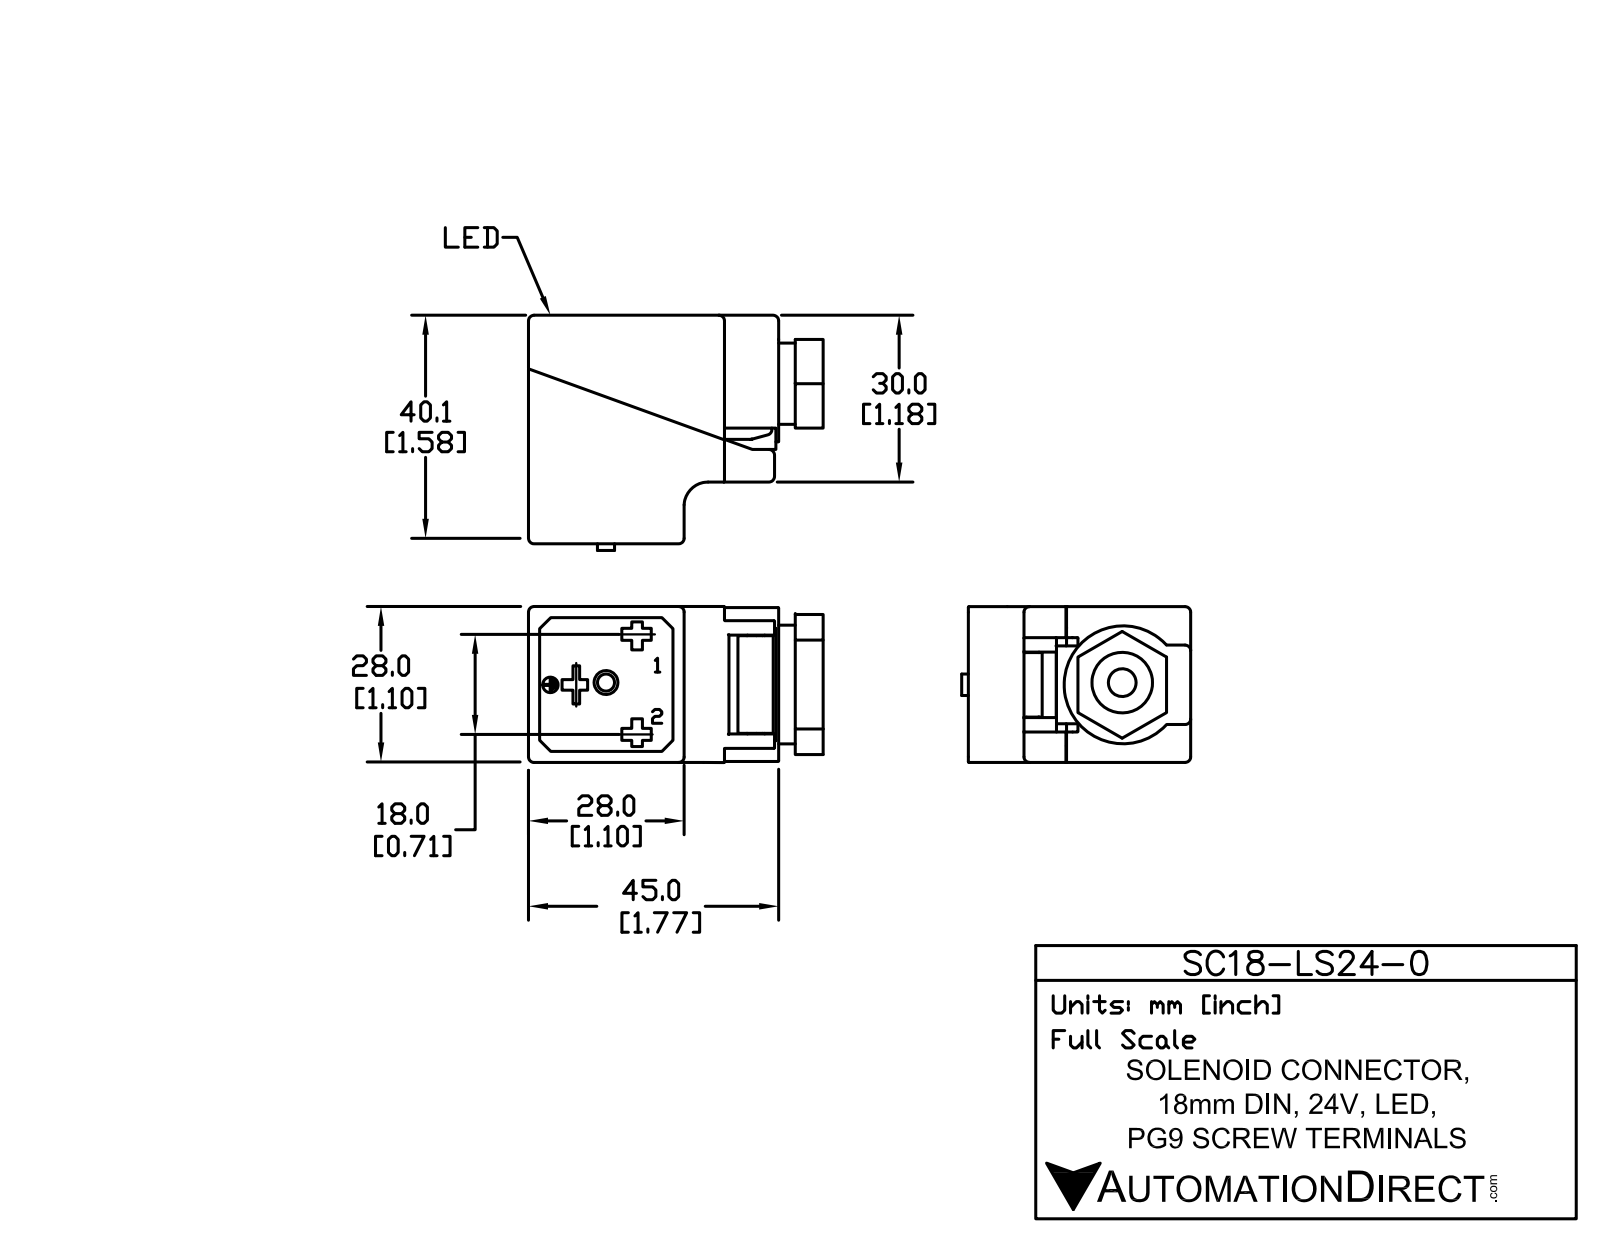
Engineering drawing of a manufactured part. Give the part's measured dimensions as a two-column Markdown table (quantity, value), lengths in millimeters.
| quantity | value |
| --- | --- |
| part name | SC18-LS24-0 |
| STEP written by | SolidWorks 2011 (AUTOMOTIVE_DESIGN) |
| units | millimeters |
| bodies | 7 solids, 501 faces (396 planar, 71 cylindrical, 34 other) |
| overall size | 53.55 × 46 × 28 |
| volume | 29 002 mm³ |
| surface area | 20 998 mm² |
| round holes (diameter × count) | 2.5 × 1, 3 × 1, 3.5 × 1, 3.75 × 1, 5.5 × 1, 5.75 × 1, 7 × 1, 9.4 × 1, 10 × 1, 10.1 × 1, 11 × 1, 14 × 1 |
| round bosses / shafts (diameter × count) | 1.5 × 2, 15 × 1, 13.5 × 1, 13.4 × 1, 11.7 × 1, 5.9 × 1, 3 × 1, 2.9 × 1 |
| partial cylindrical surfaces (radius × count) | 2 × 13, 1 × 12, 0.36 × 2, 1.5 × 2, 0.5 × 1, 1.36 × 1, 1.43 × 1, 1.5 × 1 |
| main face-to-face distances | 2.35, 23.3, 25.65, 2, 2.5, 2.3, 25.6, 2.15, 23.15, 27.95 |
| hole center spacings | 10.75, 10.96 |
